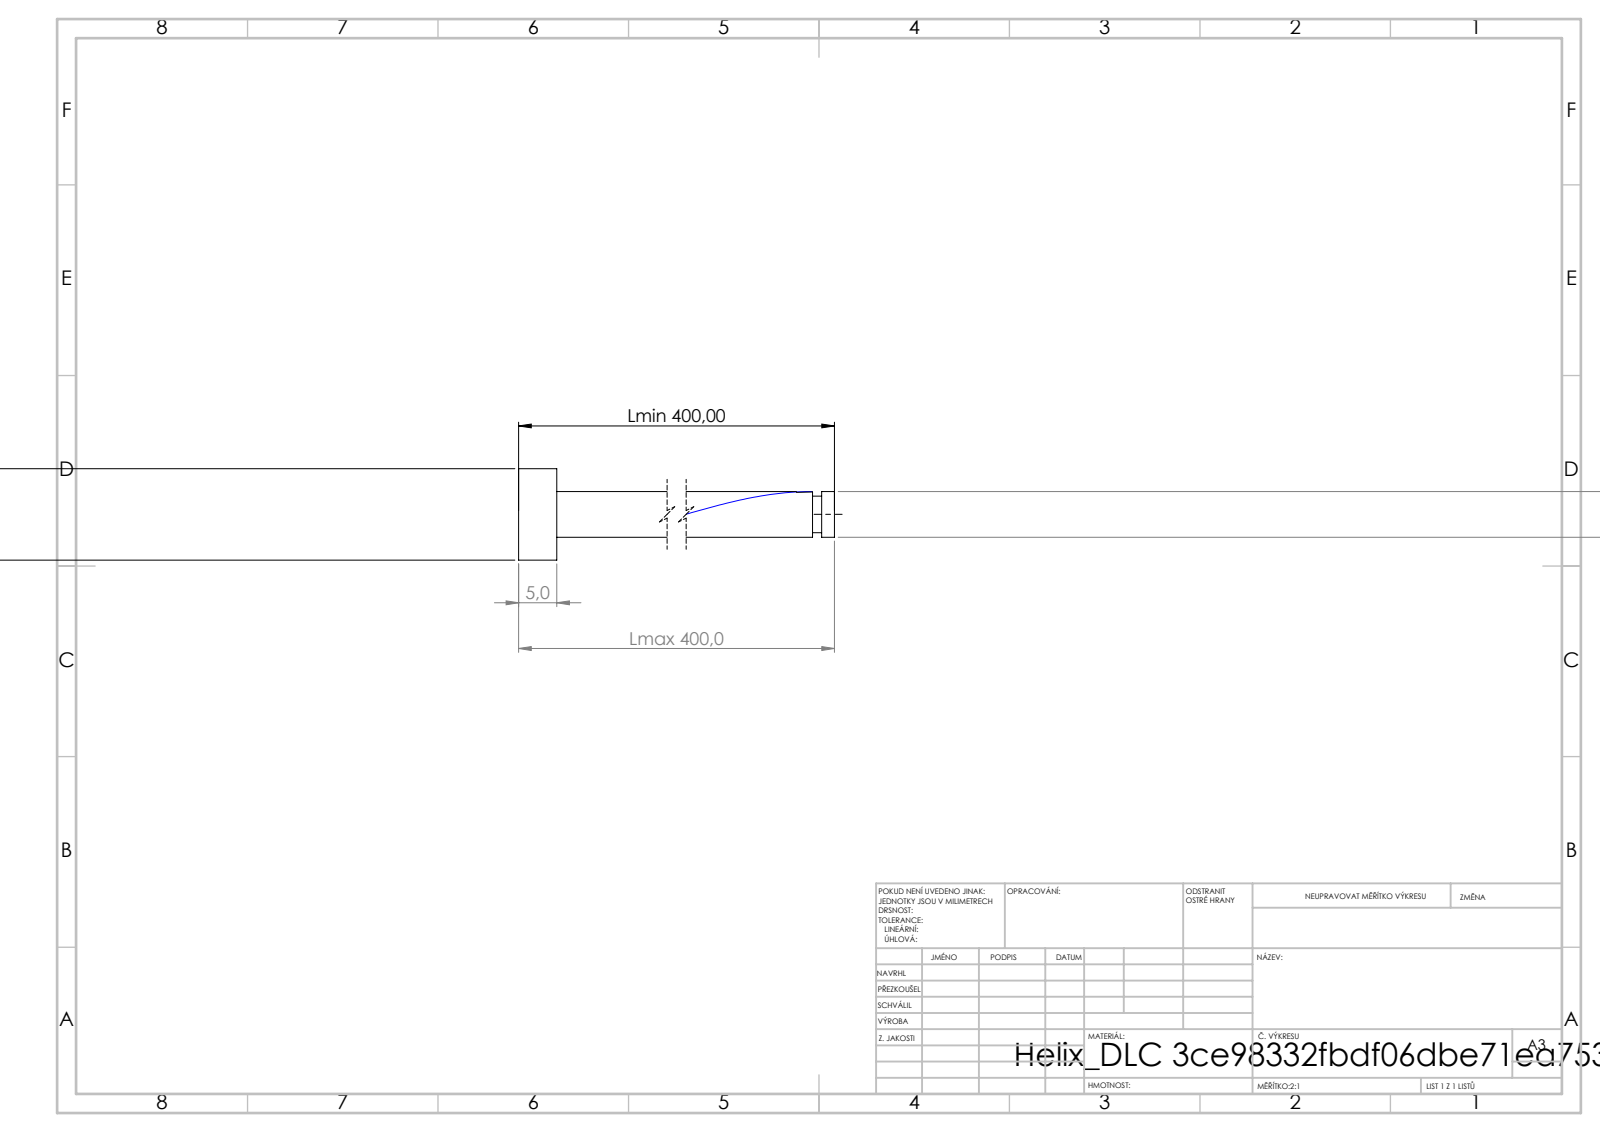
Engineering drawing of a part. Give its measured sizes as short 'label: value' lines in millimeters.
written by: SolidWorks 2019 (CONFIG_CONTROL_DESIGN)
unit: mm
bodies: 1 solid, 16 faces (6 planar, 9 cylindrical, 1 other)
size: 400 × 12 × 12
volume: 14 128 mm³; area: 10 510 mm²
bosses: 1× ⌀12, 1× ⌀6, 1× ⌀4.8
face distances: 5, 400, 395, 398.32, 393.32, 1.68, 397.12, 392.12, 1.2, 2.88
